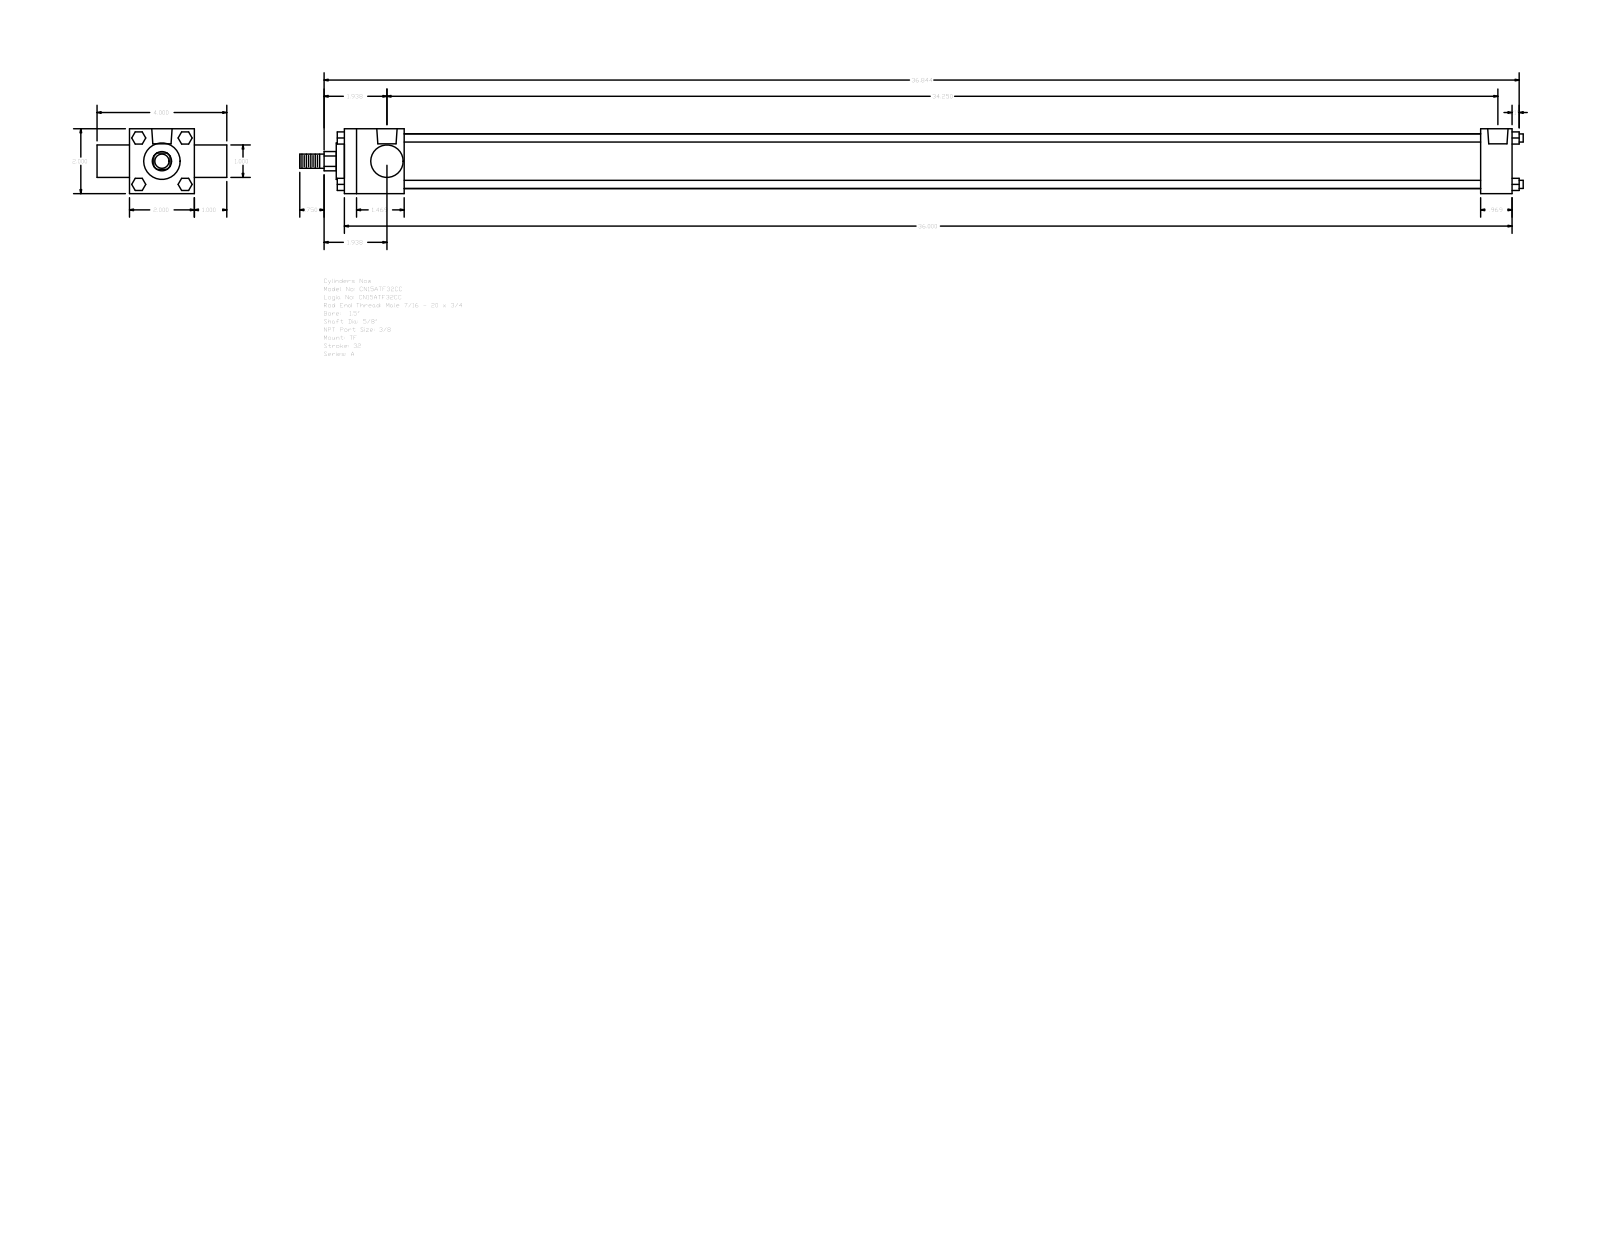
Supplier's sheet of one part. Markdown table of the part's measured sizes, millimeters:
| quantity | value |
| --- | --- |
| part name | A_TF__0150_0.625 |
| STEP written by | GSSL Pune (CONFIG_CONTROL_DESIGN) |
| units | millimeters |
| bodies | 0 solids, 120 faces (92 planar, 28 cylindrical, 0 other) |
| overall size | 958.06 × 101.6 × 50.8 |
| round holes (diameter × count) | 5.56 × 3, 15.93 × 2 |
| round bosses / shafts (diameter × count) | 6.35 × 4, 42.93 × 1, 28.57 × 1, 25.4 × 1, 15.88 × 1, 11.11 × 1 |
| partial cylindrical surfaces (radius × count) | 7.54 × 1 |
| main face-to-face distances | 50.8, 914.39, 25.4, 76.2, 46.83, 889.79, 842.96, 867.56, 24.6, 101.6 |
| hole center spacings | 3.97, 865.98, 862.01, 869.95 |
